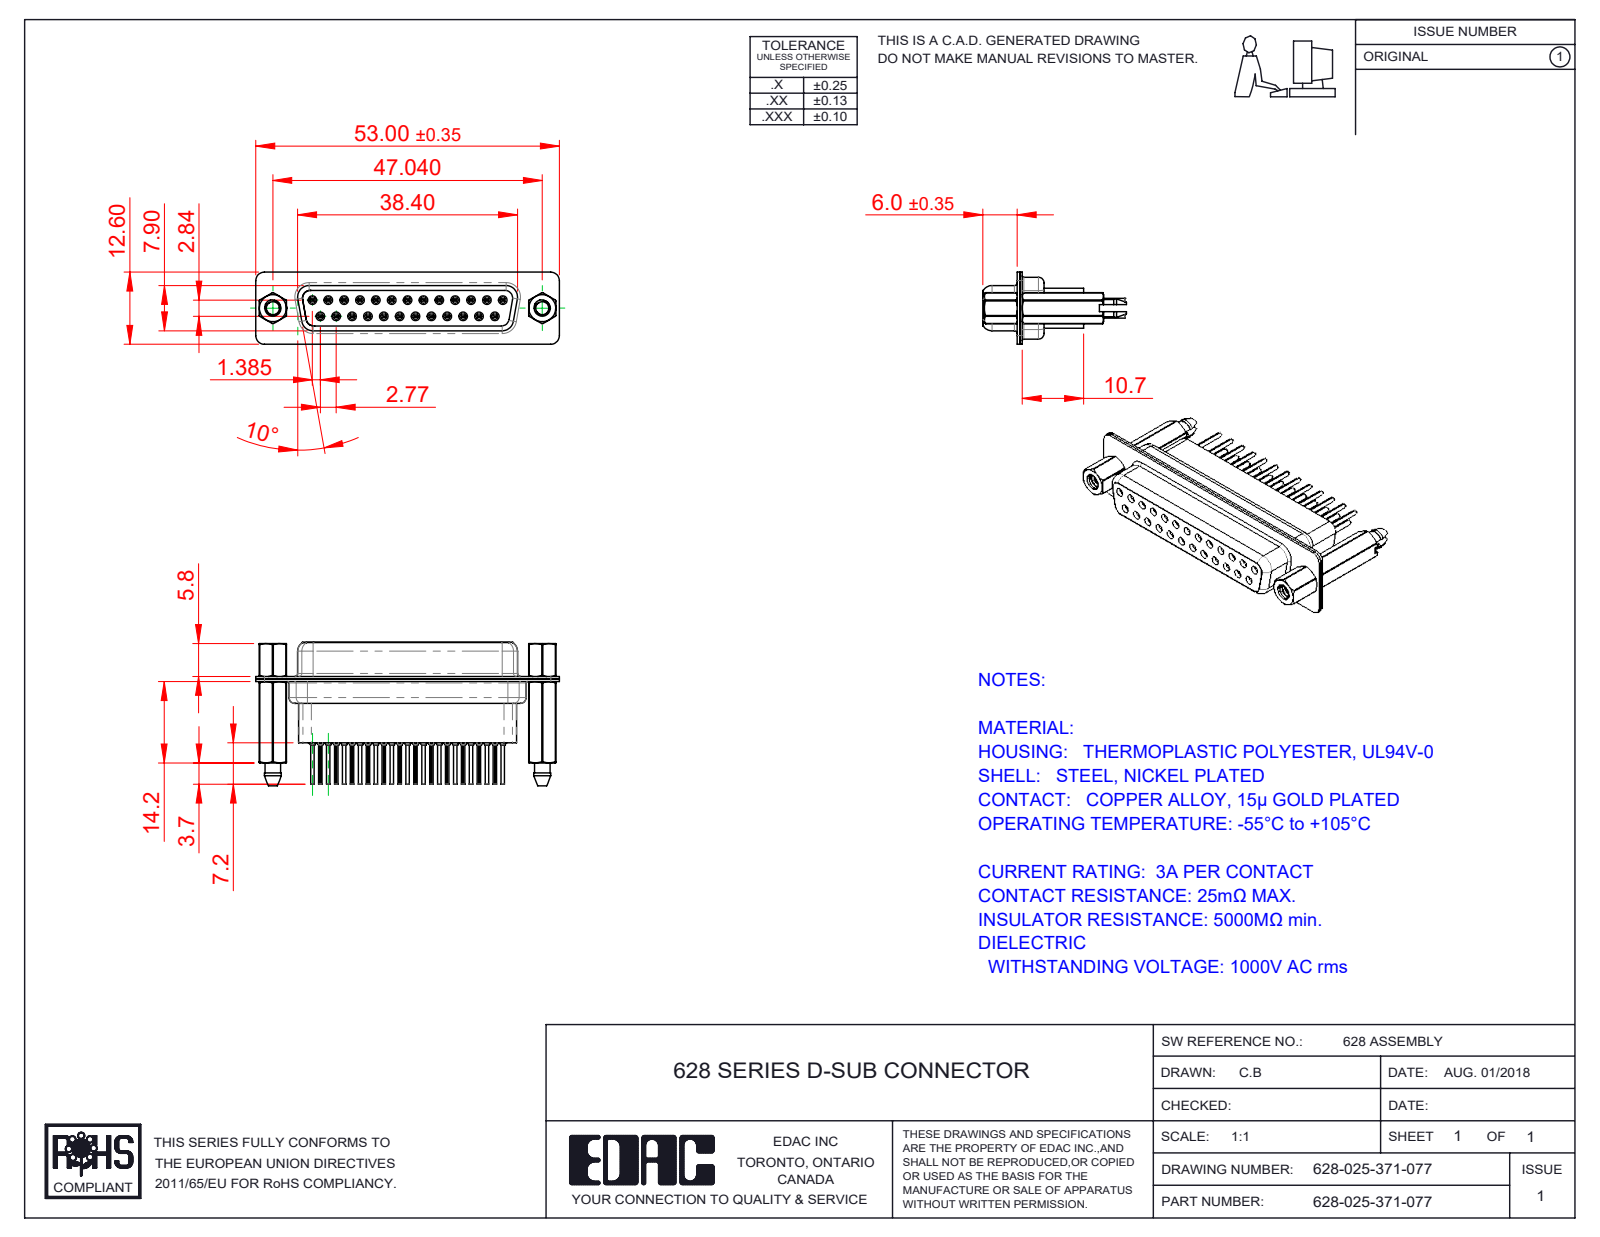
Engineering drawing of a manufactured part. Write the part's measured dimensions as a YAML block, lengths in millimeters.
part_name: "628 4-40 Threaded Boardlock_HP71; 628 4-40 Hex Standoff; 628 Shell Front_25 Contacts; 628-025-371-077 (+4 more)"
step_written_by: "SolidWorks 2020 (CONFIG_CONTROL_DESIGN)"
units: millimeters
bodies: {solids: 32, faces: 3554, planar: 896, cylindrical: 1066, other: 1592}
overall_size: [53, 25.1, 12.6]
volume: 5587
surface_area: 12849
round_holes:
  - {diameter: 0.2, count: 25}
  - {diameter: 0.8, count: 25}
  - {diameter: 0.9, count: 25}
  - {diameter: 1.1, count: 25}
  - {diameter: 1.6, count: 25}
  - {diameter: 1.7, count: 13}
  - {diameter: 2.26, count: 2}
  - {diameter: 2.29, count: 2}
  - {diameter: 4, count: 2}
  - {diameter: 4.05, count: 2}
  - {diameter: 4.85, count: 2}
round_bosses_or_shafts:
  - {diameter: 2, count: 25}
  - {diameter: 1.5, count: 25}
  - {diameter: 1.2, count: 25}
  - {diameter: 0.6, count: 25}
  - {diameter: 4.95, count: 2}
  - {diameter: 4.8, count: 2}
  - {diameter: 2.79, count: 2}
partial_cylinders:
  - {radius: 0.1, count: 50}
  - {radius: 0.28, count: 25}
  - {radius: 1.5, count: 18}
  - {radius: 2, count: 12}
  - {radius: 1.35, count: 6}
  - {radius: 1.6, count: 6}
  - {radius: 0.25, count: 4}
  - {radius: 0.5, count: 4}
face_to_face_distances: [0.45, 0.4, 6.6, 8.5, 1.9, 7, 0.9, 4.76, 1.4, 7.05]
hole_center_spacings: [3.16, 8.31, 2.77, 5.54, 11.08, 16.62, 5.03, 5.04]
